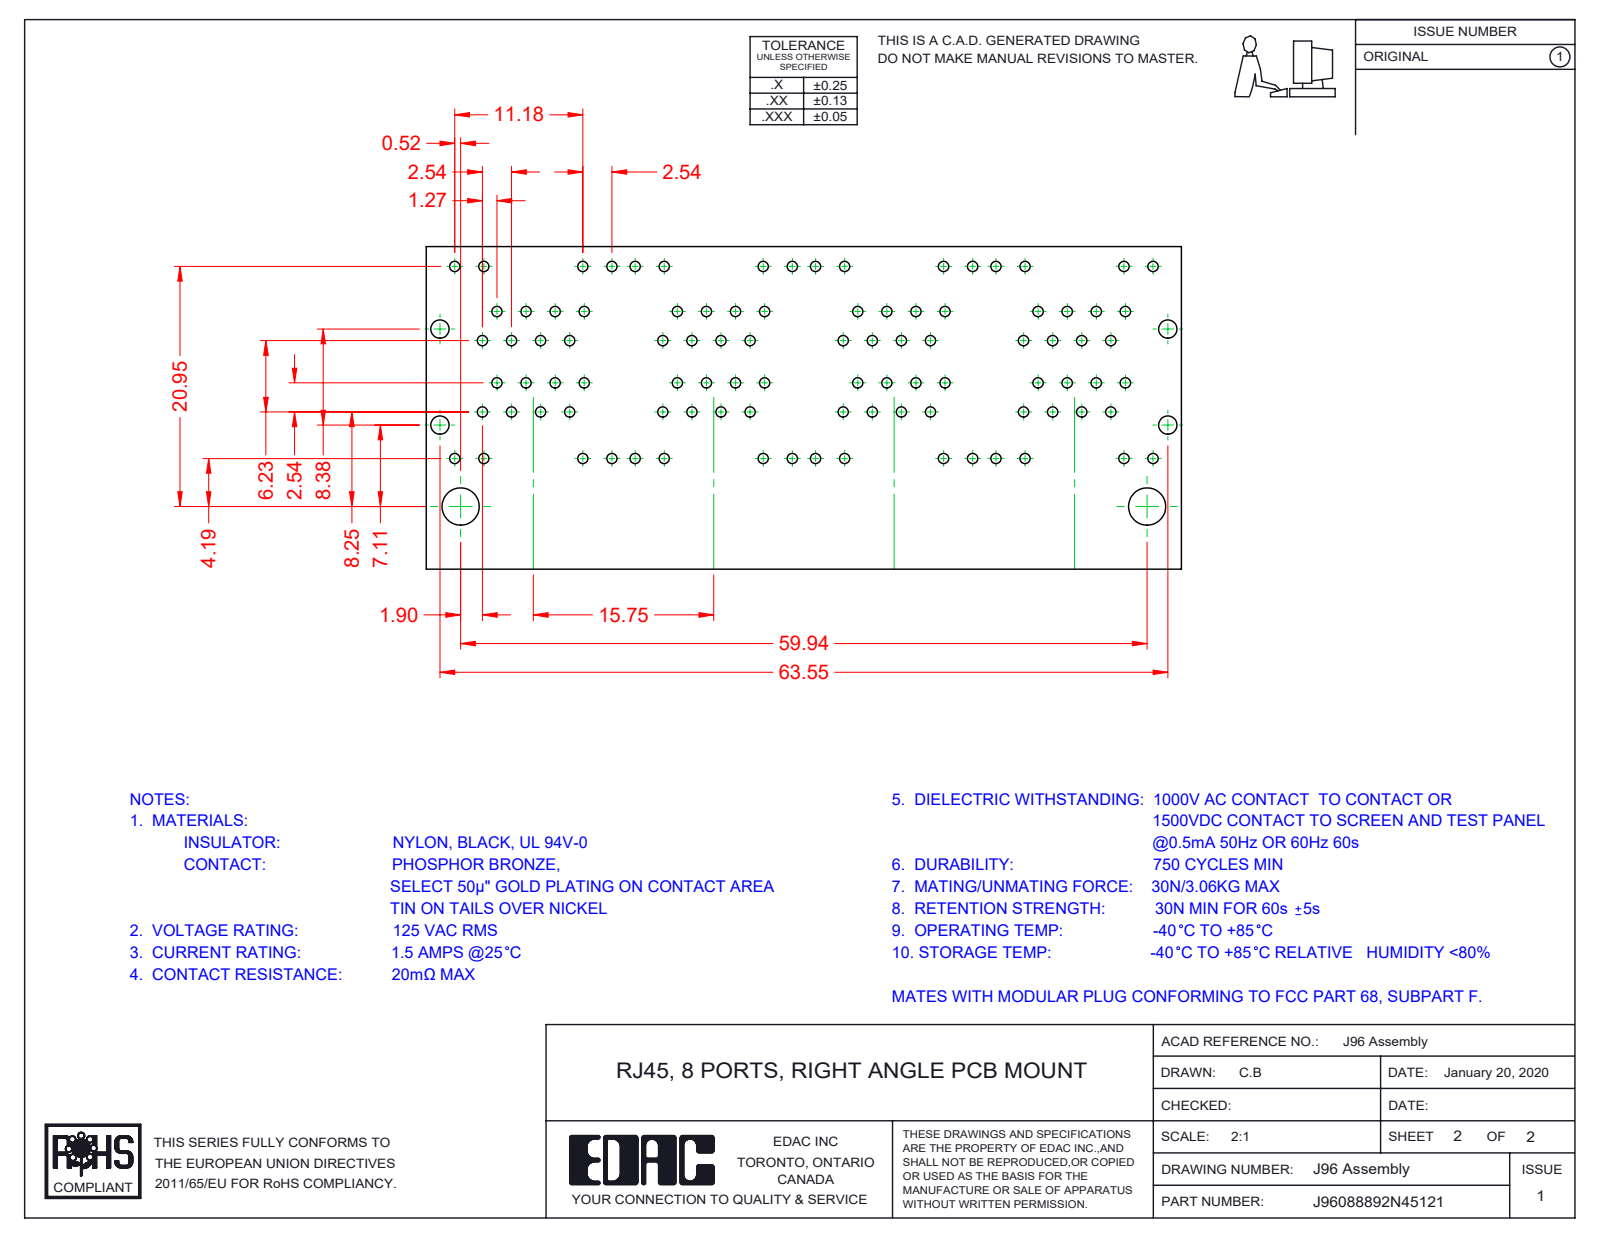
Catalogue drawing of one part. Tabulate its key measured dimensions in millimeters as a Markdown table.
| quantity | value |
| --- | --- |
| part name | 96 Insulator Insert; 96 Back Plate_8 Ports; 96 Contacts Lower; 96 LED RH Upper_5-Green-Yellow (+8 more) |
| STEP written by | SolidWorks 2016 (CONFIG_CONTROL_DESIGN) |
| units | millimeters |
| bodies | 96 solids, 7658 faces (6069 planar, 1323 cylindrical, 266 other) |
| overall size | 64.05 × 29.58 × 28.68 |
| volume | 24 160 mm³ |
| surface area | 63 658 mm² |
| round holes (diameter × count) | 1.7 × 3 |
| round bosses / shafts (diameter × count) | 1.68 × 3 |
| partial cylindrical surfaces (radius × count) | 0.25 × 124, 0.35 × 73, 1 × 72, 0.5 × 49, 0.91 × 32, 0.2 × 21, 0.7 × 11, 0.22 × 8 |
| main face-to-face distances | 15.75, 0.35, 9.95, 1.17, 1.6, 0.54, 9.98, 10.18, 12.67, 3.37 |
| hole center spacings | 15.75, 31.5 |
